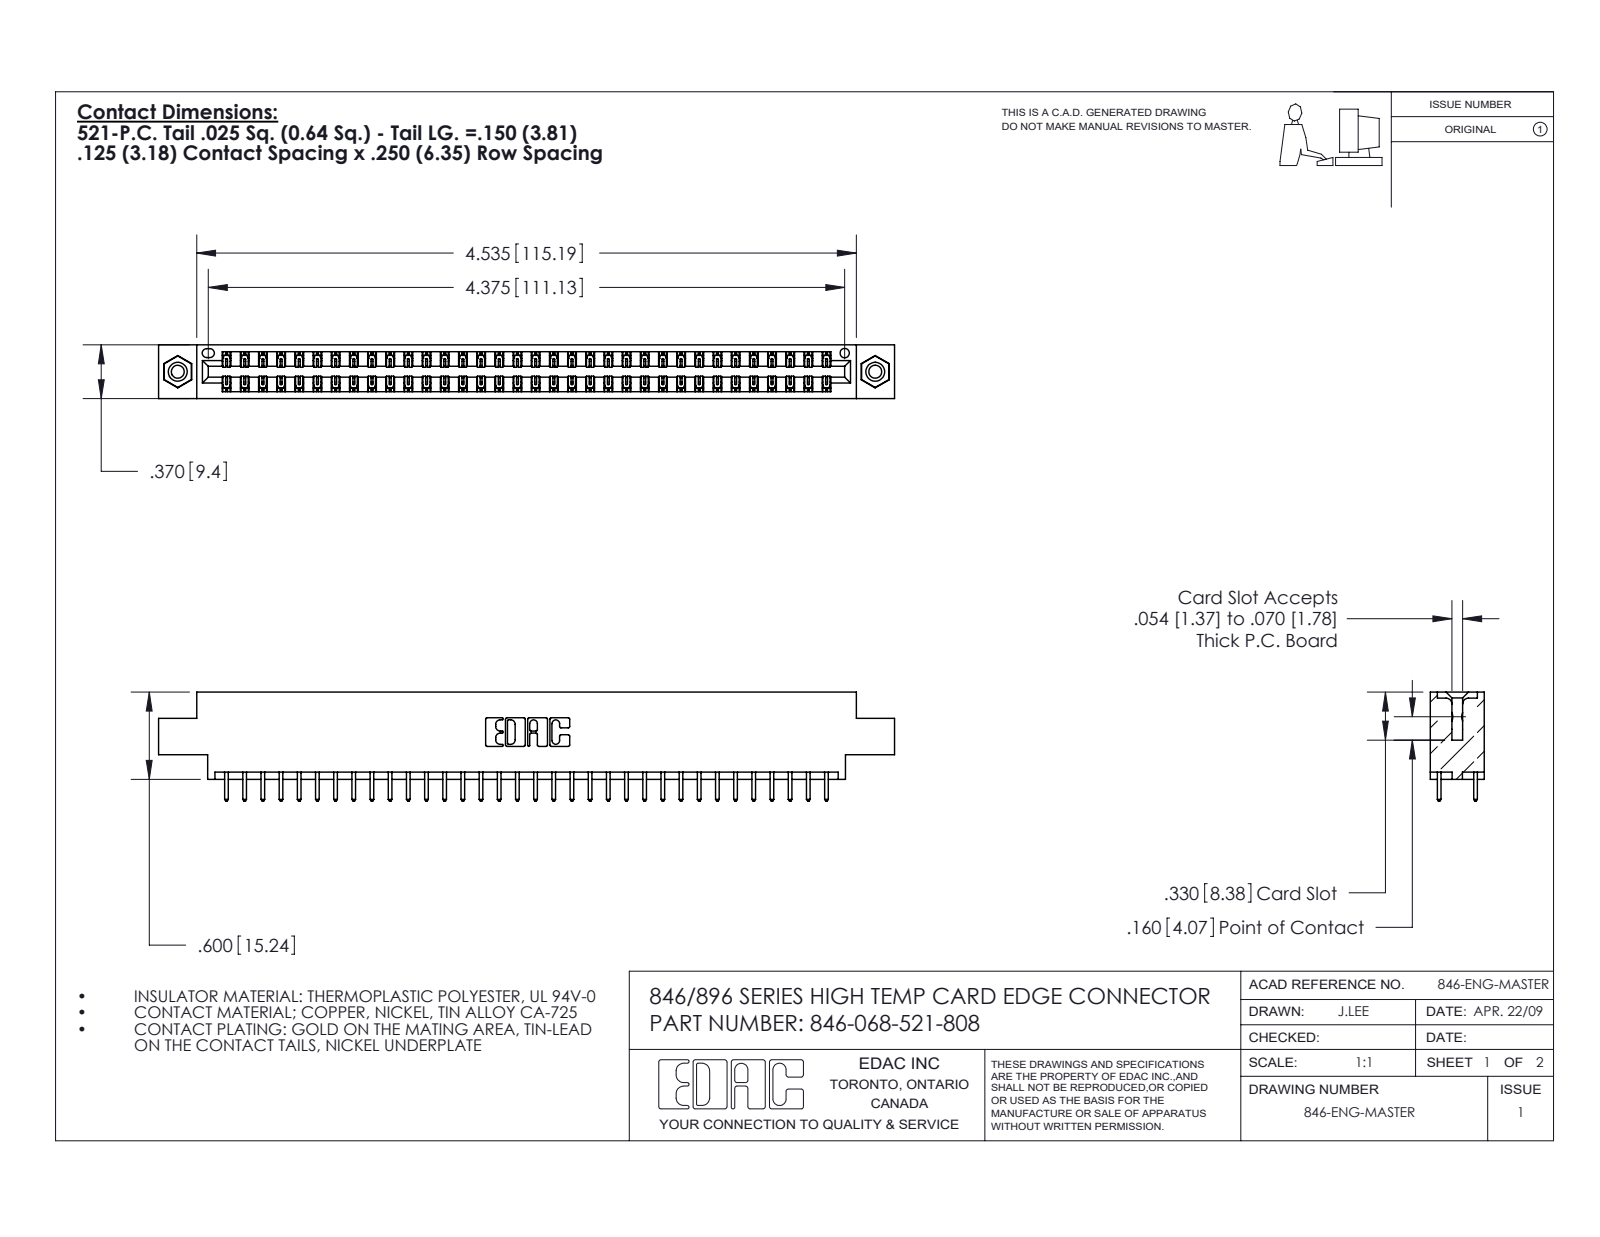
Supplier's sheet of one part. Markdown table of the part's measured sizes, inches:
| quantity | value |
| --- | --- |
| part name | 346 Part_0.170 Offset - 0.156 Dia-TI; 345-250-001_345-250-003-102; 346-068-521-808; 345-292-001_345-293-121 |
| STEP written by | SolidWorks 2016 (CONFIG_CONTROL_DESIGN) |
| units | inches |
| bodies | 71 solids, 3722 faces (2492 planar, 1214 cylindrical, 16 other) |
| overall size | 5.06 × 0.75 × 0.37 |
| volume | 0.749 in³ |
| surface area | 25.99 in² |
| round holes (diameter × count) | 0.089 × 2, 0.125 × 2, 0.156 × 2, 0.064 × 1 |
| round bosses / shafts (diameter × count) | 0.155 × 2 |
| partial cylindrical surfaces (radius × count) | 0.006 × 102, 0.01 × 68, 0.01 × 22, 0.007 × 6, 0.031 × 6, 0.026 × 3, 0.014 × 2, 0.022 × 2 |
| main face-to-face distances | 0.048, 0.322, 0.37, 0.25, 0.072, 0.298, 0.025, 0.275, 0.222, 0.148 |
| hole center spacings | 0.246, 4.587, 4.795 |
